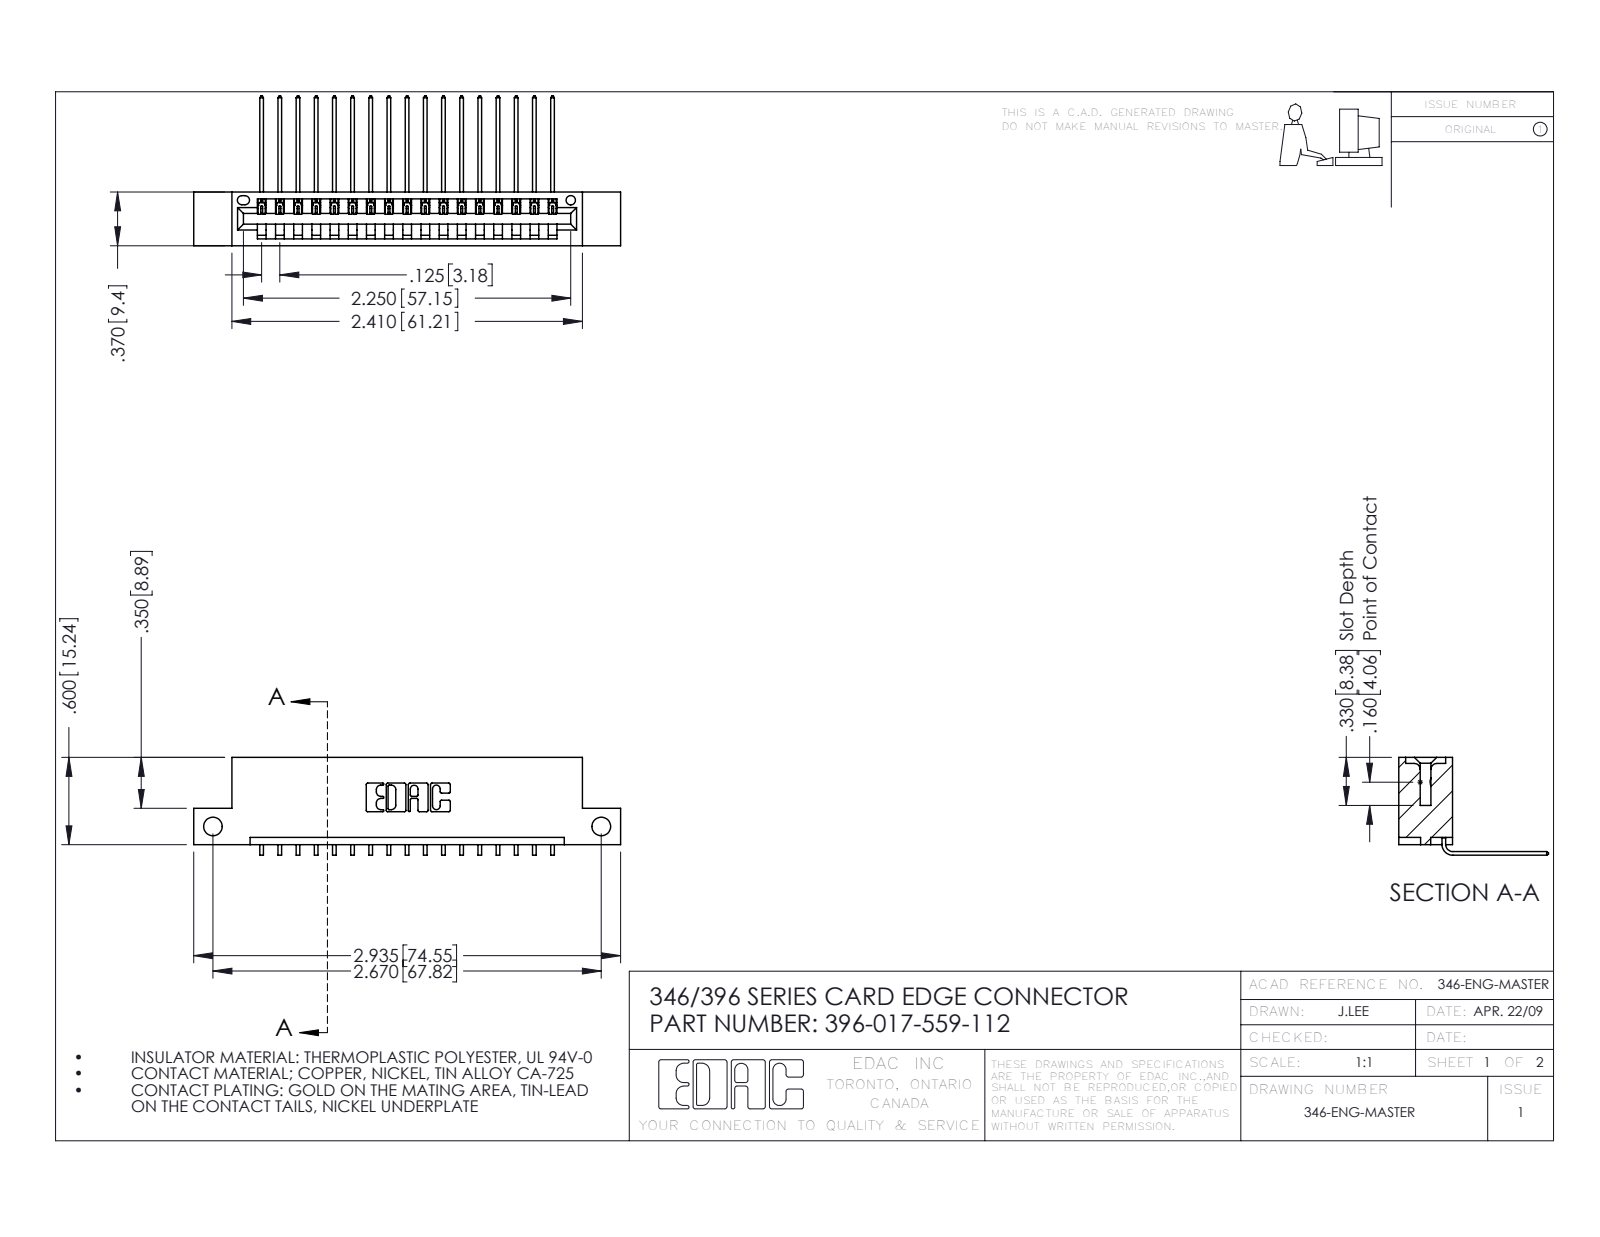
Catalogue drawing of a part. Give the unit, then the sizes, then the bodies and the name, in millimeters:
Units: millimetres
Overall size (bounding box): 74.5 × 26.2 × 17.1
Round holes (diameter × count): ⌀3.3 ×2, ⌀1.6 ×1
Partial cylindrical surfaces — rounded edges, fillets, slot ends (radius × count): R0.2 ×34, R0.3 ×22, R0.2 ×6, R0.8 ×6, R0.7 ×3, R0.8 ×2, R1 ×2, R0.4 ×1
Main face-to-face distances: 1.2, 8.2, 6.4, 9.4, 1.8, 0.6, 7.6, 3.8, 5.6, 2.5
Hole centre spacings: 67.8
Volume: 6 930 mm³ · Surface area: 8 587 mm²
Bodies: 18 solids, 1142 faces (790 planar, 352 cylindrical, 0 other)
Part name (STEP PRODUCT): 396-017-559-112; 346 Part_Flush Mounting Lugs - Side Mount; 345-292-001_558 559 Tail - 1
STEP written by: SolidWorks 2016 (CONFIG_CONTROL_DESIGN)
